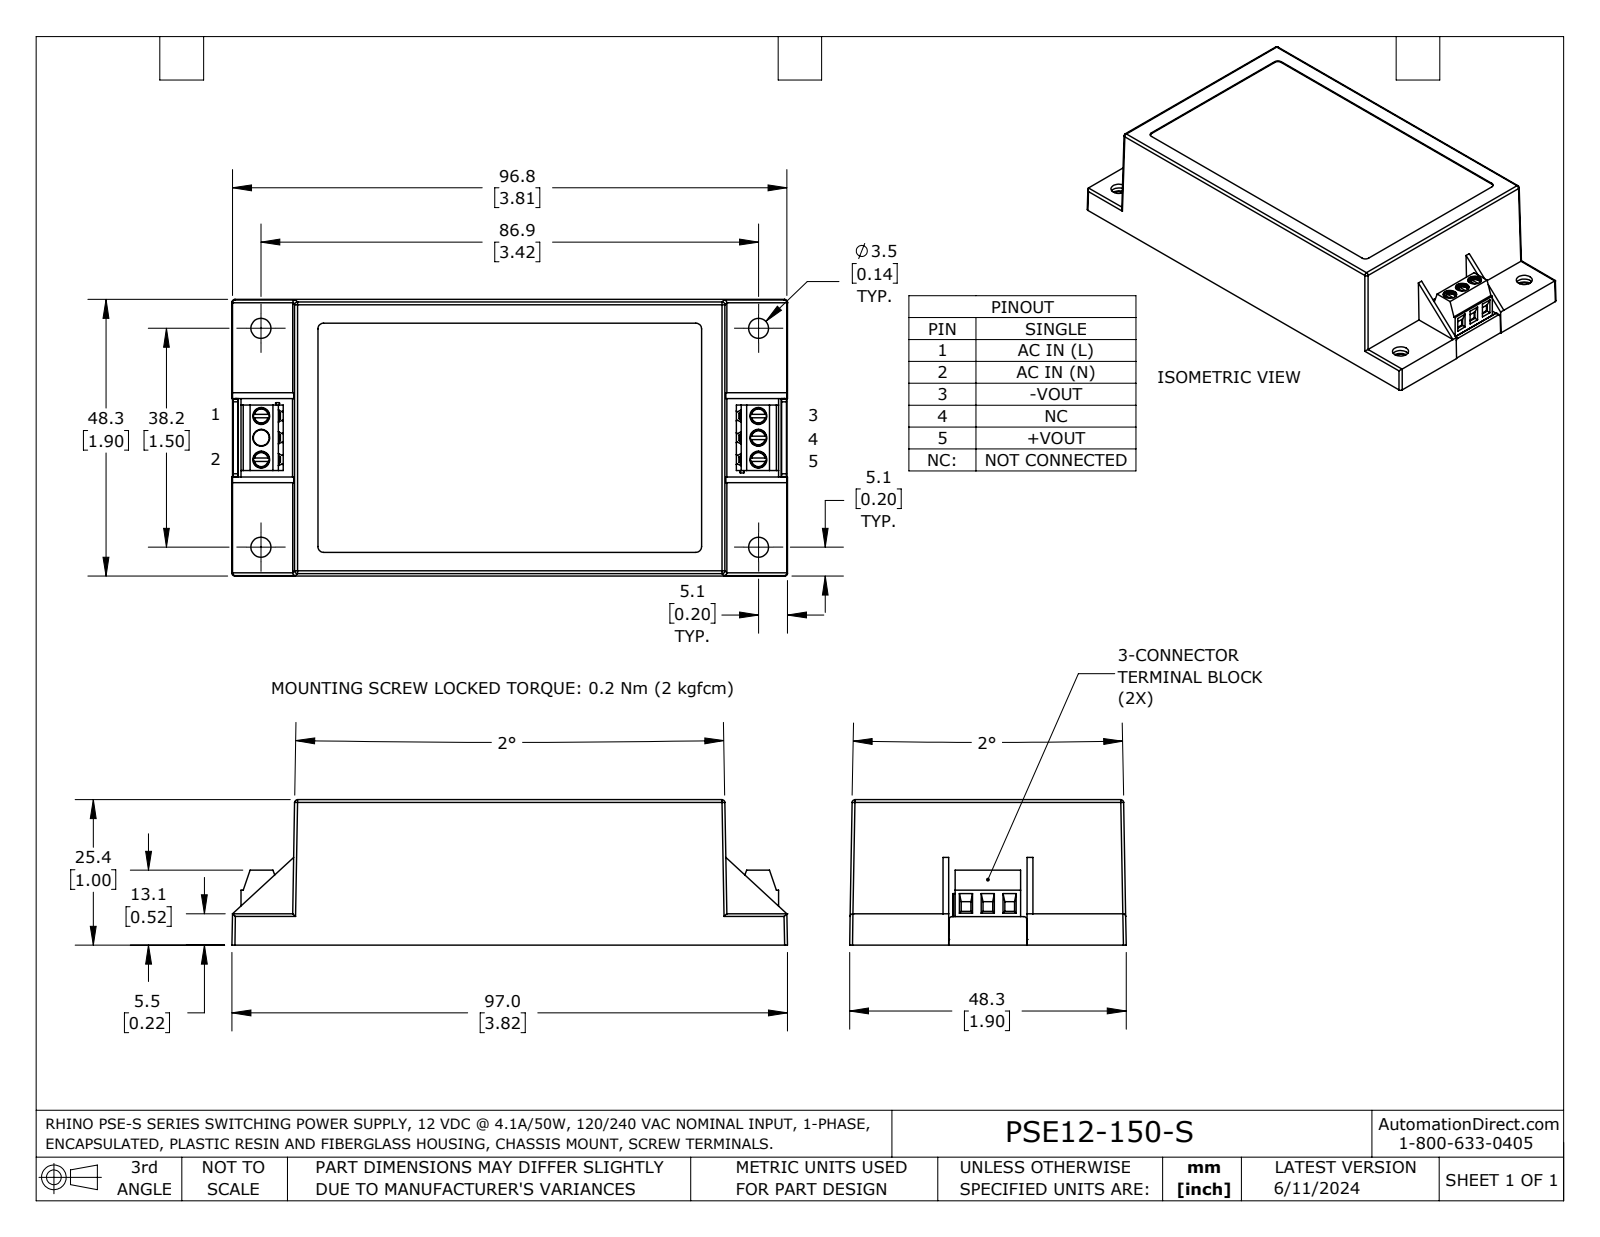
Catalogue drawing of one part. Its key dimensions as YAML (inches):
part_name: "PSE12-150-S"
step_written_by: "SolidWorks 2023 (AUTOMOTIVE_DESIGN)"
units: inches
bodies: {solids: 5, faces: 560, planar: 396, cylindrical: 130, other: 34}
overall_size: [3.819, 1.902, 1]
volume: 1.175
surface_area: 63.85
round_holes:
  - {diameter: 0.116, count: 6}
  - {diameter: 0.138, count: 4}
  - {diameter: 0.161, count: 4}
  - {diameter: 0.11, count: 1}
partial_cylinders:
  - {radius: 0.009, count: 18}
  - {radius: 0.02, count: 18}
  - {radius: 0.006, count: 12}
  - {radius: 0.004, count: 8}
  - {radius: 0.008, count: 4}
  - {radius: 0.01, count: 4}
  - {radius: 0.039, count: 4}
  - {radius: 0.079, count: 4}
face_to_face_distances: [0.039, 0.138, 0.815, 0.953, 0.177, 0.098, 0.776, 0.913, 0.854, 0.992]
hole_center_spacings: [0.15, 3.42, 3.417, 0.3, 0.602, 0.602, 0.752, 0.752]
